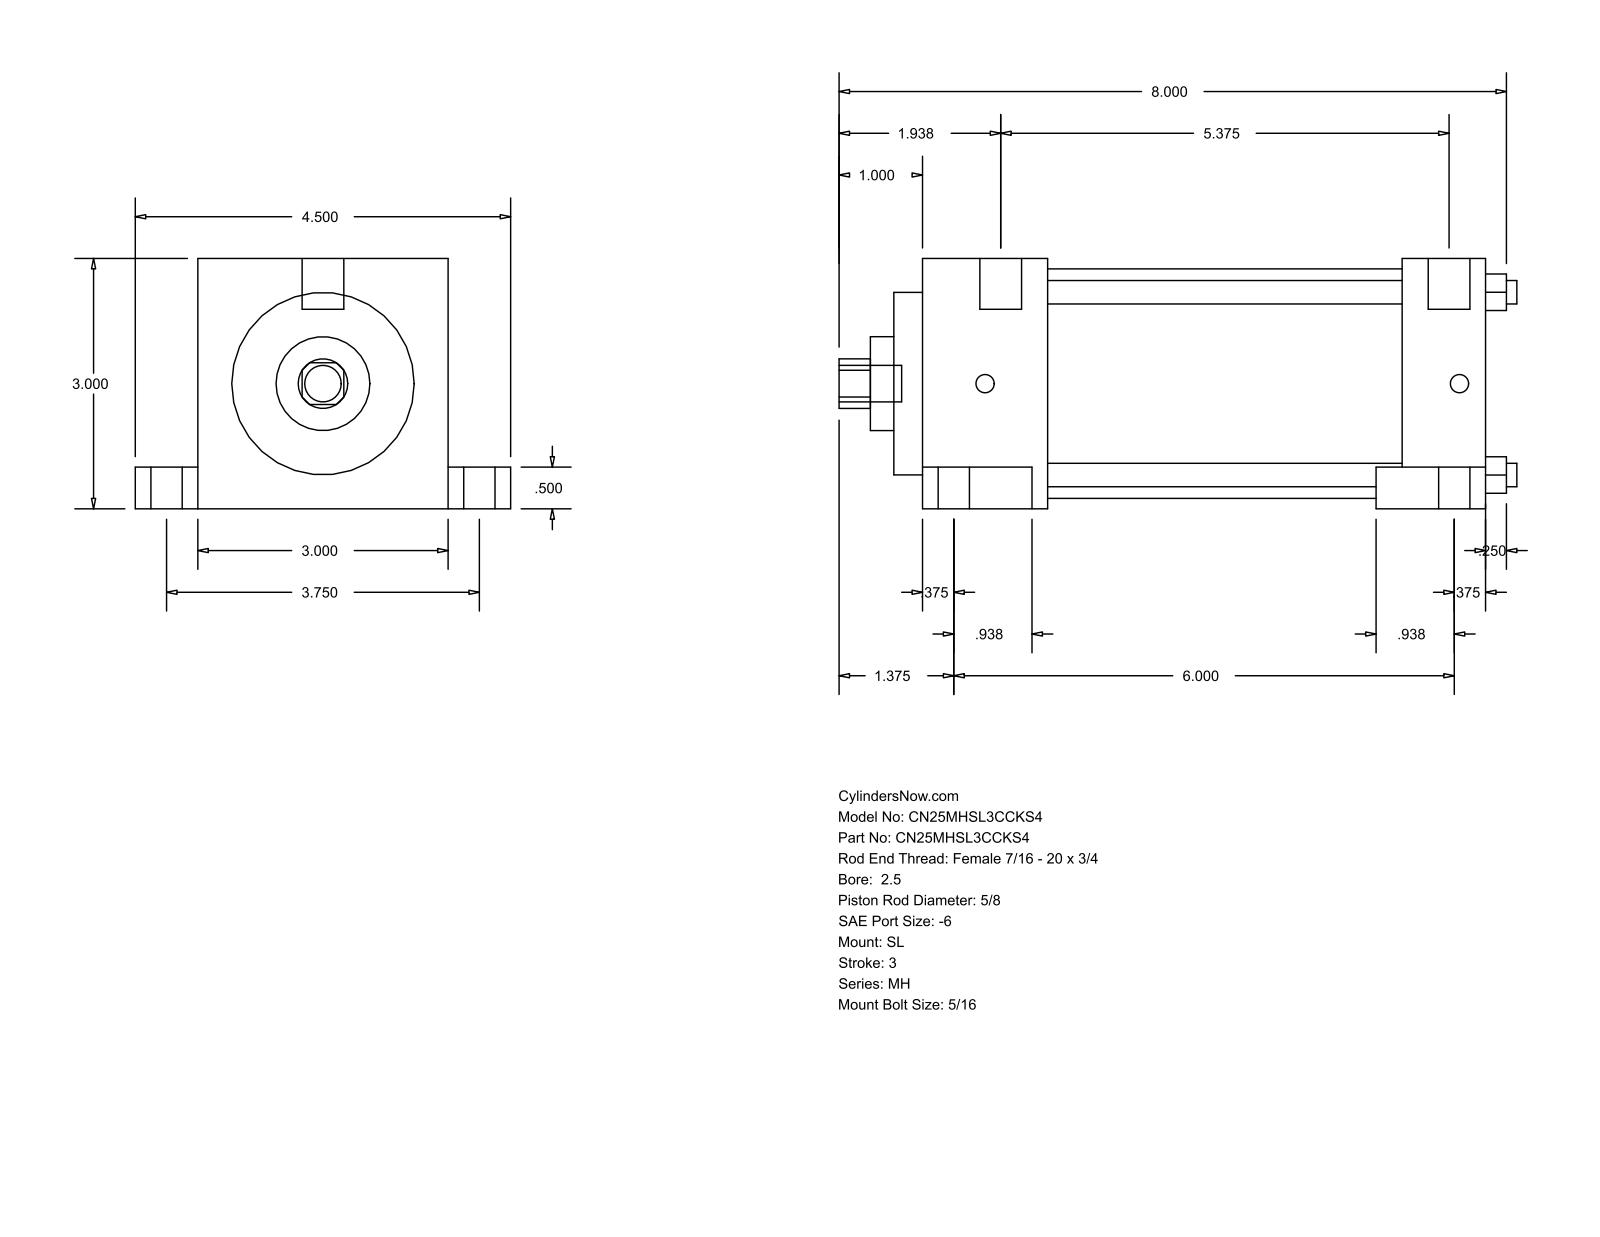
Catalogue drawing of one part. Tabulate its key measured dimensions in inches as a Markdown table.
| quantity | value |
| --- | --- |
| part name | MH_SL__0250_0.625 |
| STEP written by | GSSL Pune (CONFIG_CONTROL_DESIGN) |
| units | inches |
| bodies | 0 solids, 86 faces (61 planar, 25 cylindrical, 0 other) |
| overall size | 8.125 × 4.5 × 3 |
| round holes (diameter × count) | 0.281 × 4, 0.625 × 1, 1.125 × 1, 2.187 × 1, 2.75 × 1 |
| round bosses / shafts (diameter × count) | 0.625 × 2, 0.375 × 2, 0.219 × 2, 0.5 × 1, 0.437 × 1 |
| partial cylindrical surfaces (radius × count) | 0.297 × 1 |
| main face-to-face distances | 3, 1, 6.094, 7.094, 0.5, 2.5, 0.75, 3.75, 1.25, 5.781 |
| hole center spacings | 1.548, 2.19, 3.097 |
